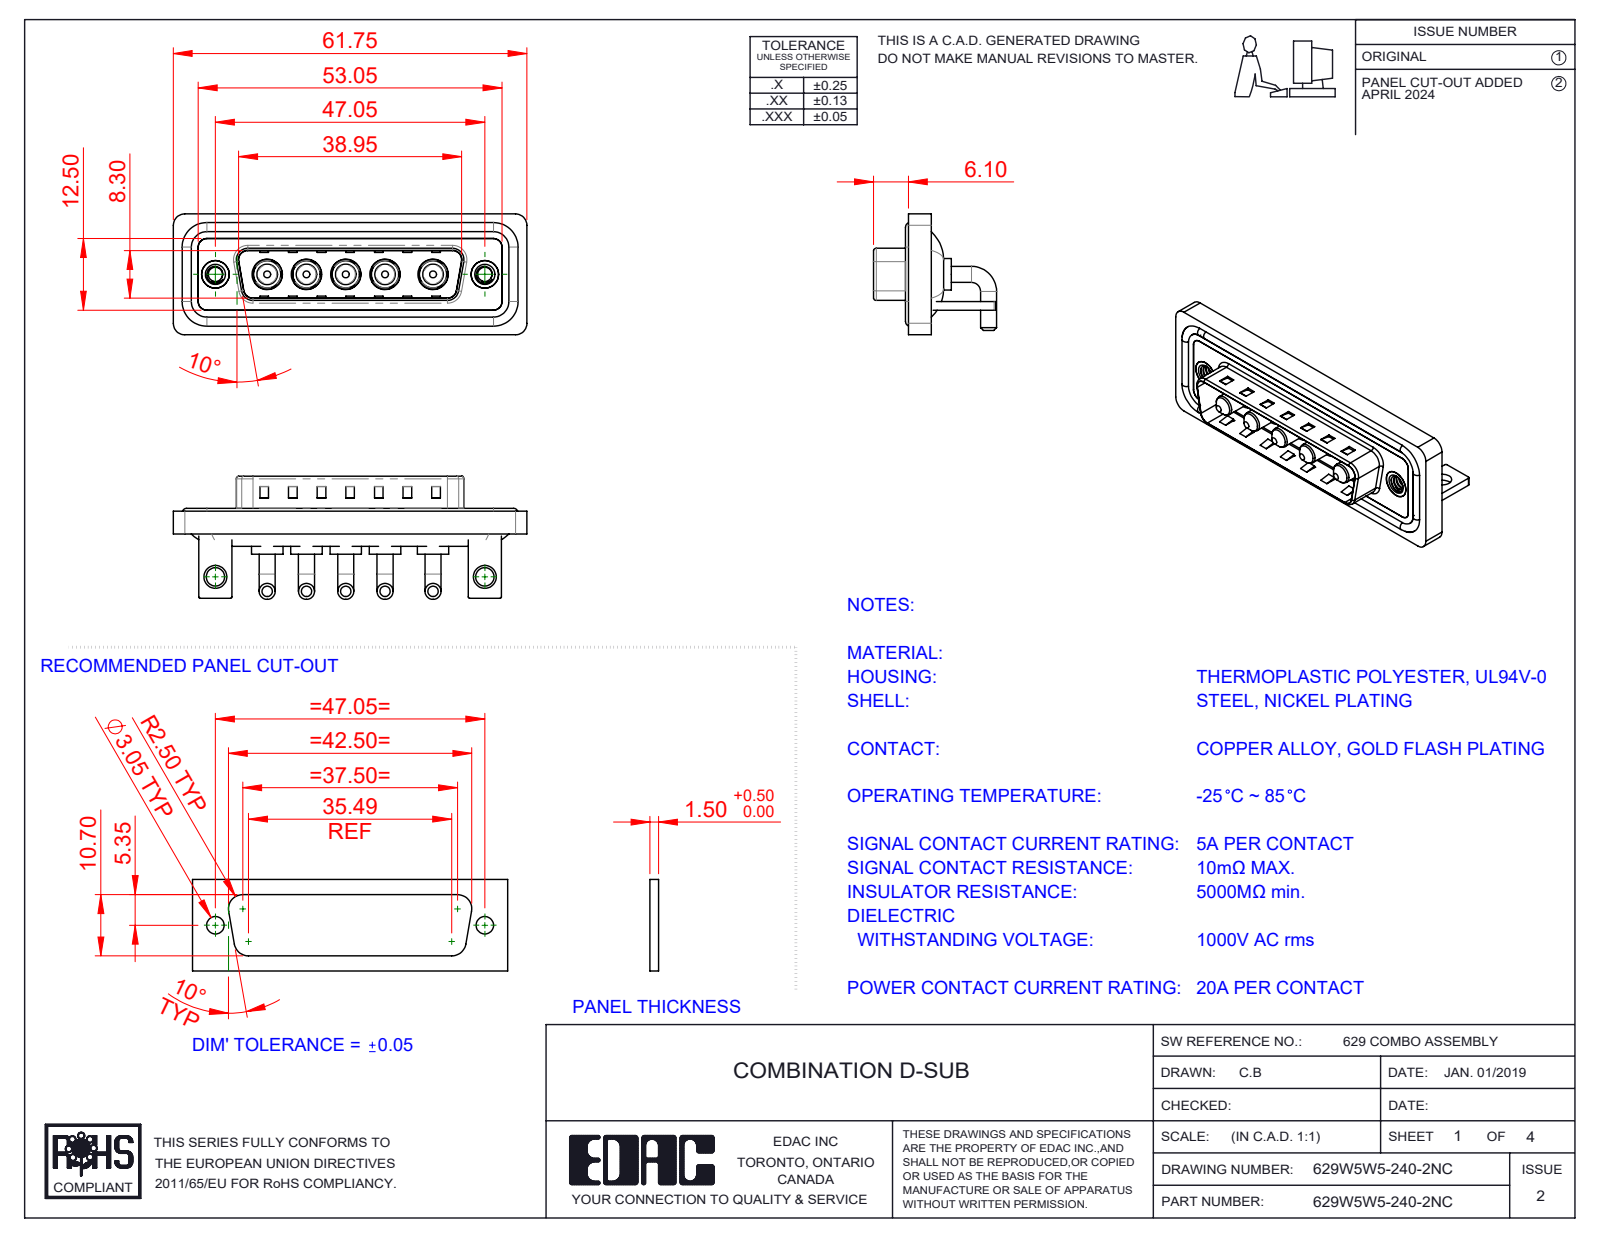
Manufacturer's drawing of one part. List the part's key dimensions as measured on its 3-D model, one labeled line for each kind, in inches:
Part name (STEP PRODUCT): 629Combo Waterproof Housing_25 Contacts; 629Combo Housing_5W5; 629Combo Shell Rear_25 Contacts; 629Combo Stabilizer Bracket (+4 more)
STEP written by: SolidWorks 2023 (CONFIG_CONTROL_DESIGN)
Units: inches
Bodies: 19 solids, 736 faces (279 planar, 311 cylindrical, 146 other)
Overall size (bounding box): 2.431 × 0.846 × 0.831
Volume: 0.493 in³ · Surface area: 19.93 in²
Round holes (diameter × count): ⌀0.191 ×5, ⌀0.209 ×5, ⌀0.098 ×2, ⌀0.126 ×2, ⌀0.157 ×2, ⌀0.189 ×2, ⌀0.197 ×2
Round bosses / shafts (diameter × count): ⌀0.11 ×10, ⌀0.217 ×5, ⌀0.205 ×5, ⌀0.187 ×5, ⌀0.148 ×5, ⌀0.142 ×5, ⌀0.063 ×4, ⌀0.193 ×2
Partial cylindrical surfaces — rounded edges, fillets, slot ends (radius × count): R0.079 ×19, R0.059 ×18, R0.01 ×16, R0.02 ×9, R0.063 ×8, R0.083 ×5, R0.024 ×4, R0.026 ×4
Main face-to-face distances: 0.016, 0.059, 0.114, 0.031, 0.083, 0.146, 0.043, 0.177, 0.161, 0.047
Hole centre spacings: 0.27, 0.541, 1.852, 0.27, 0.27, 0.33, 0.33, 0.356
